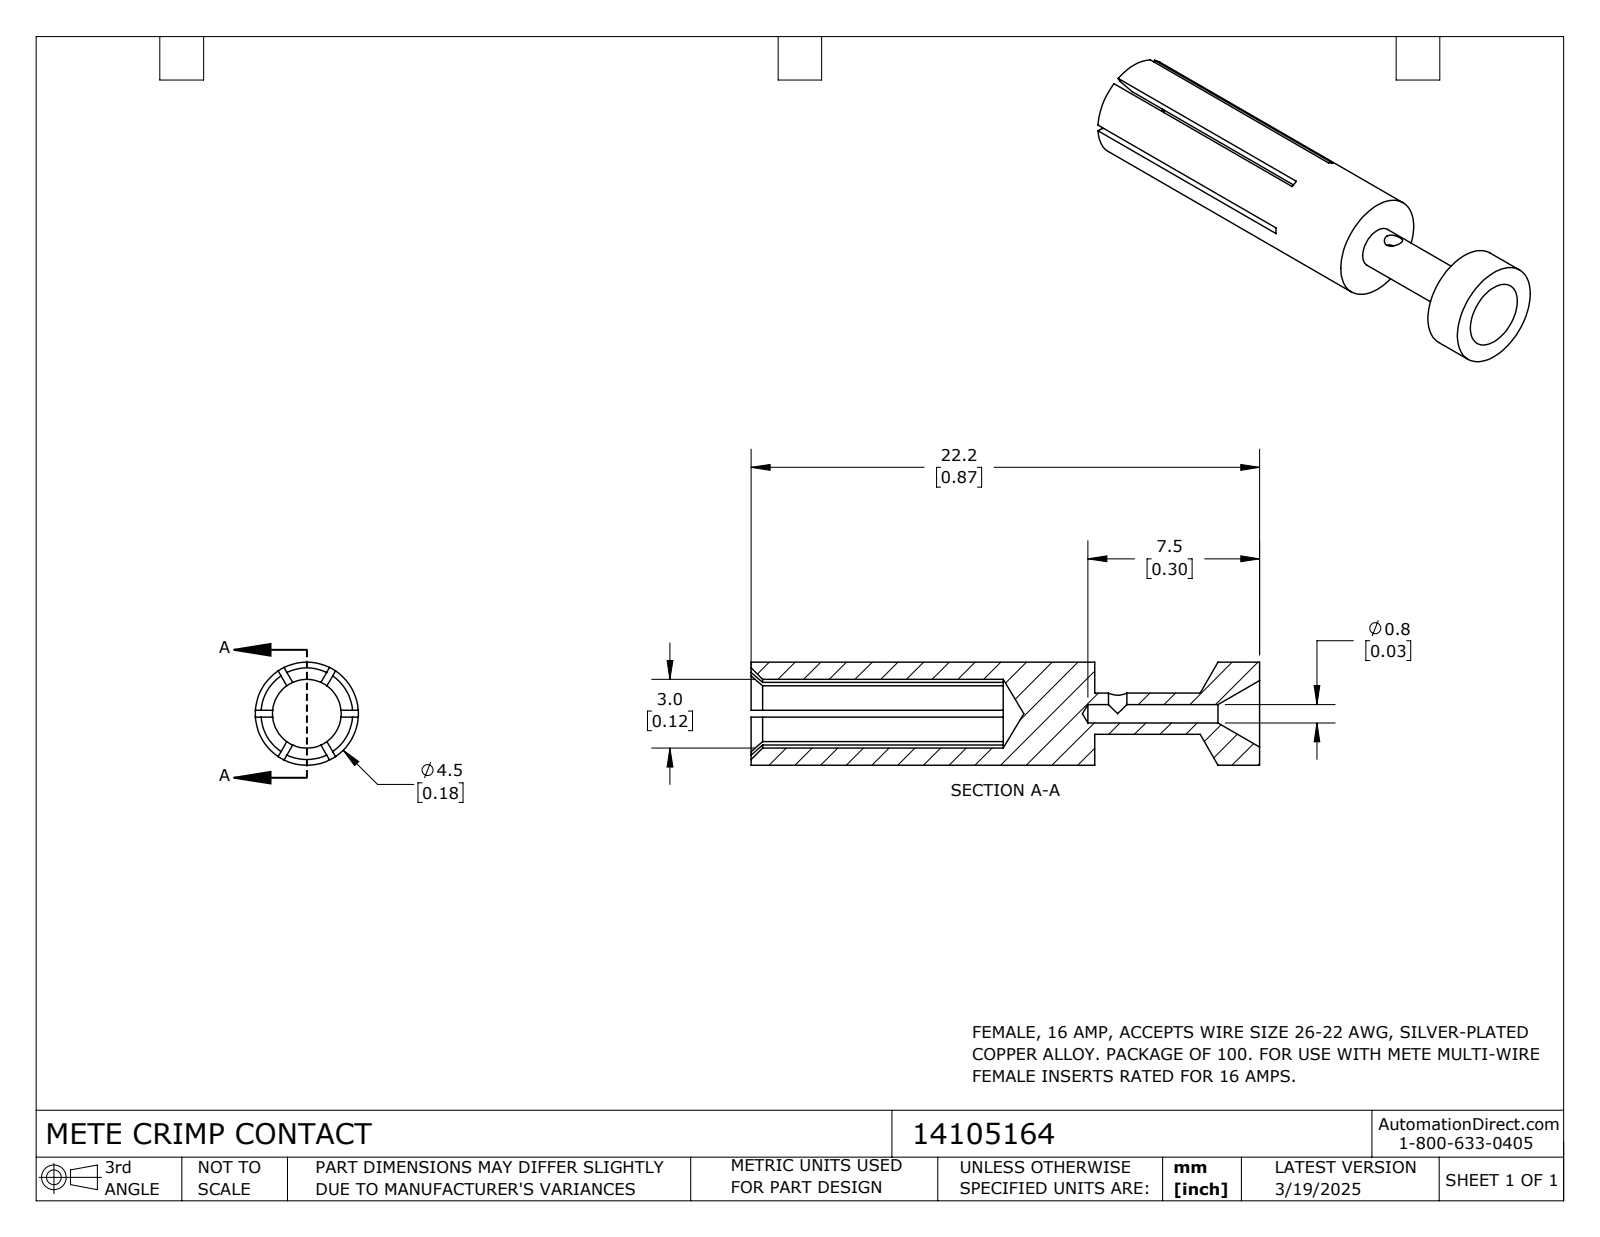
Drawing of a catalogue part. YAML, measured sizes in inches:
part_name: "14105164"
step_written_by: "SolidWorks 2024 (CONFIG_CONTROL_DESIGN)"
units: inches
bodies: {solids: 1, faces: 57, planar: 26, cylindrical: 17, other: 14}
overall_size: [0.874, 0.177, 0.177]
volume: 0.011
surface_area: 0.784
round_holes:
  - {diameter: 0.031, count: 2}
  - {diameter: 0.118, count: 1}
round_bosses_or_shafts:
  - {diameter: 0.177, count: 1}
  - {diameter: 0.071, count: 1}
face_to_face_distances: [0.283, 0.874, 0.591, 0.441, 0.157, 0.433]
